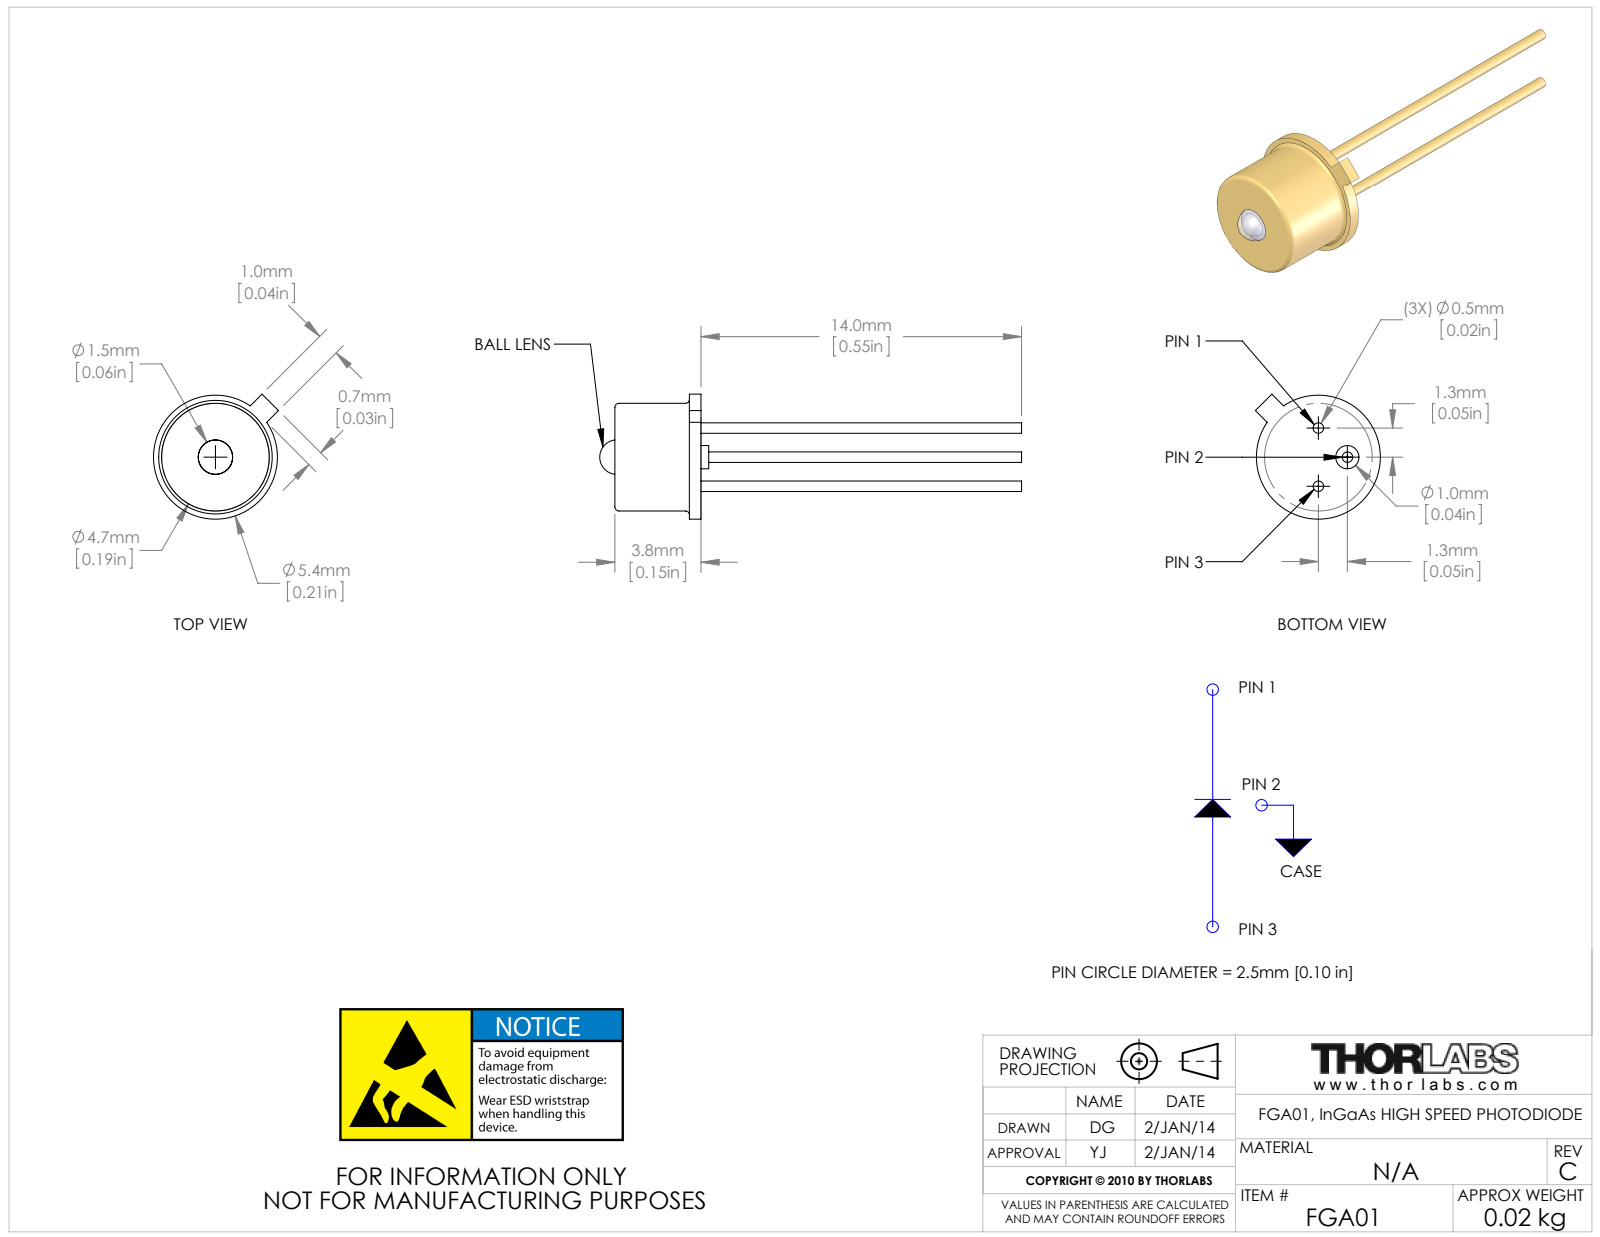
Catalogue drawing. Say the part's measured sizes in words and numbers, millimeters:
The part is named "TTN019860-E01". Its 3-D file was written by "SolidWorks 2012 (AUTOMOTIVE_DESIGN)". It is 2 solids with 38 faces: 13 planar, 17 cylindrical and 8 other. Overall it measures 18.4 by 5.5 by 5.5 millimeters. Its volume is 30 cubic millimeters and its surface area 239 square millimeters. Round holes: 1 of diameter 1.5, 1 of diameter 4.4. Round bosses or shafts: 3 of diameter 0.5, 1 of diameter 5.4, 1 of diameter 4.7, 1 of diameter 1. The main face-to-face distances are 0.5, 3.8, 3.3, 3.6, 3.1, 0.3, 0.8, 4, 4.1, 13.7.
